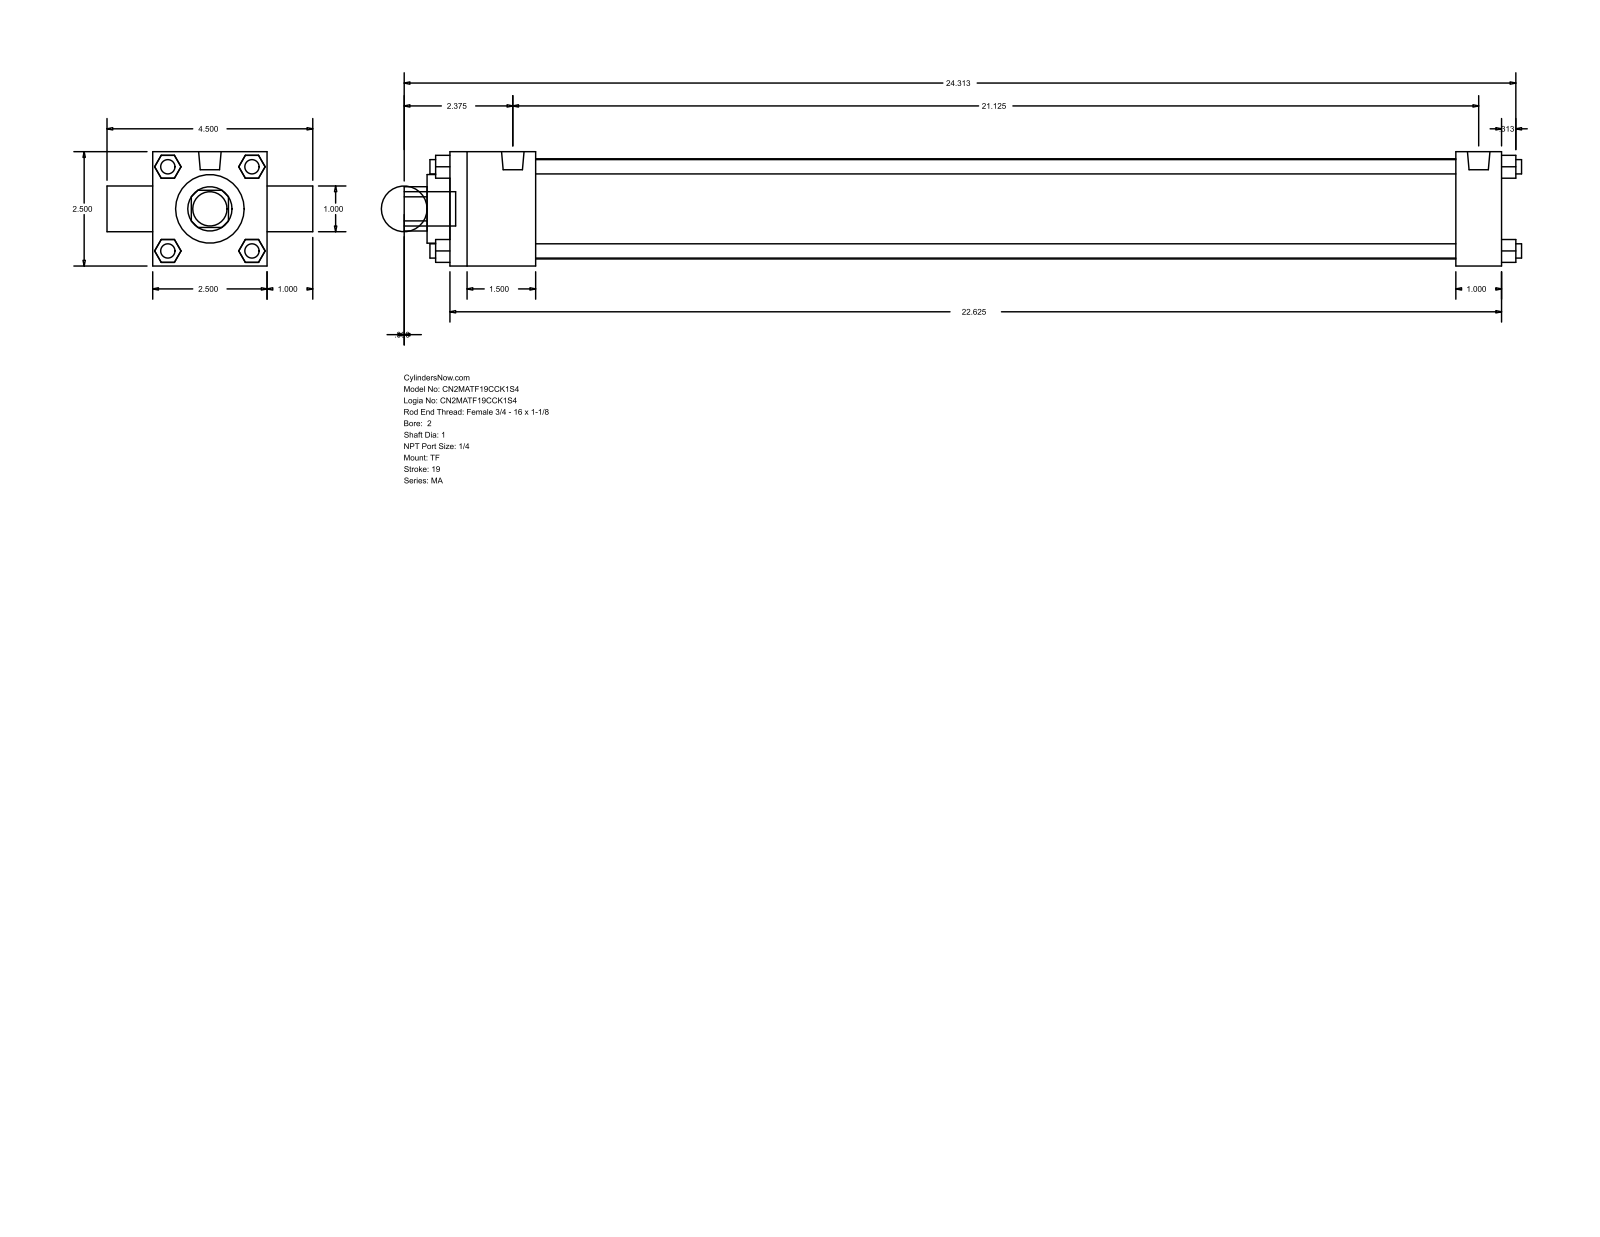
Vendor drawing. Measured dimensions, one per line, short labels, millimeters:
name: MA_TF__0200_1
written by: GSSL Pune (CONFIG_CONTROL_DESIGN)
unit: mm
bodies: 0 solids, 120 faces (92 planar, 28 cylindrical, 0 other)
size: 620.71 × 114.3 × 63.5
holes: 2× ⌀25.4, 1× ⌀38.1, 1× ⌀55.63
bosses: 7× ⌀7.94, 2× ⌀12.49, 1× ⌀19.05
rounds: 1× R12.29
face distances: 63.5, 25.4, 584.2, 12.7, 47.63, 558.8, 511.17, 536.57, 88.9, 40.47
